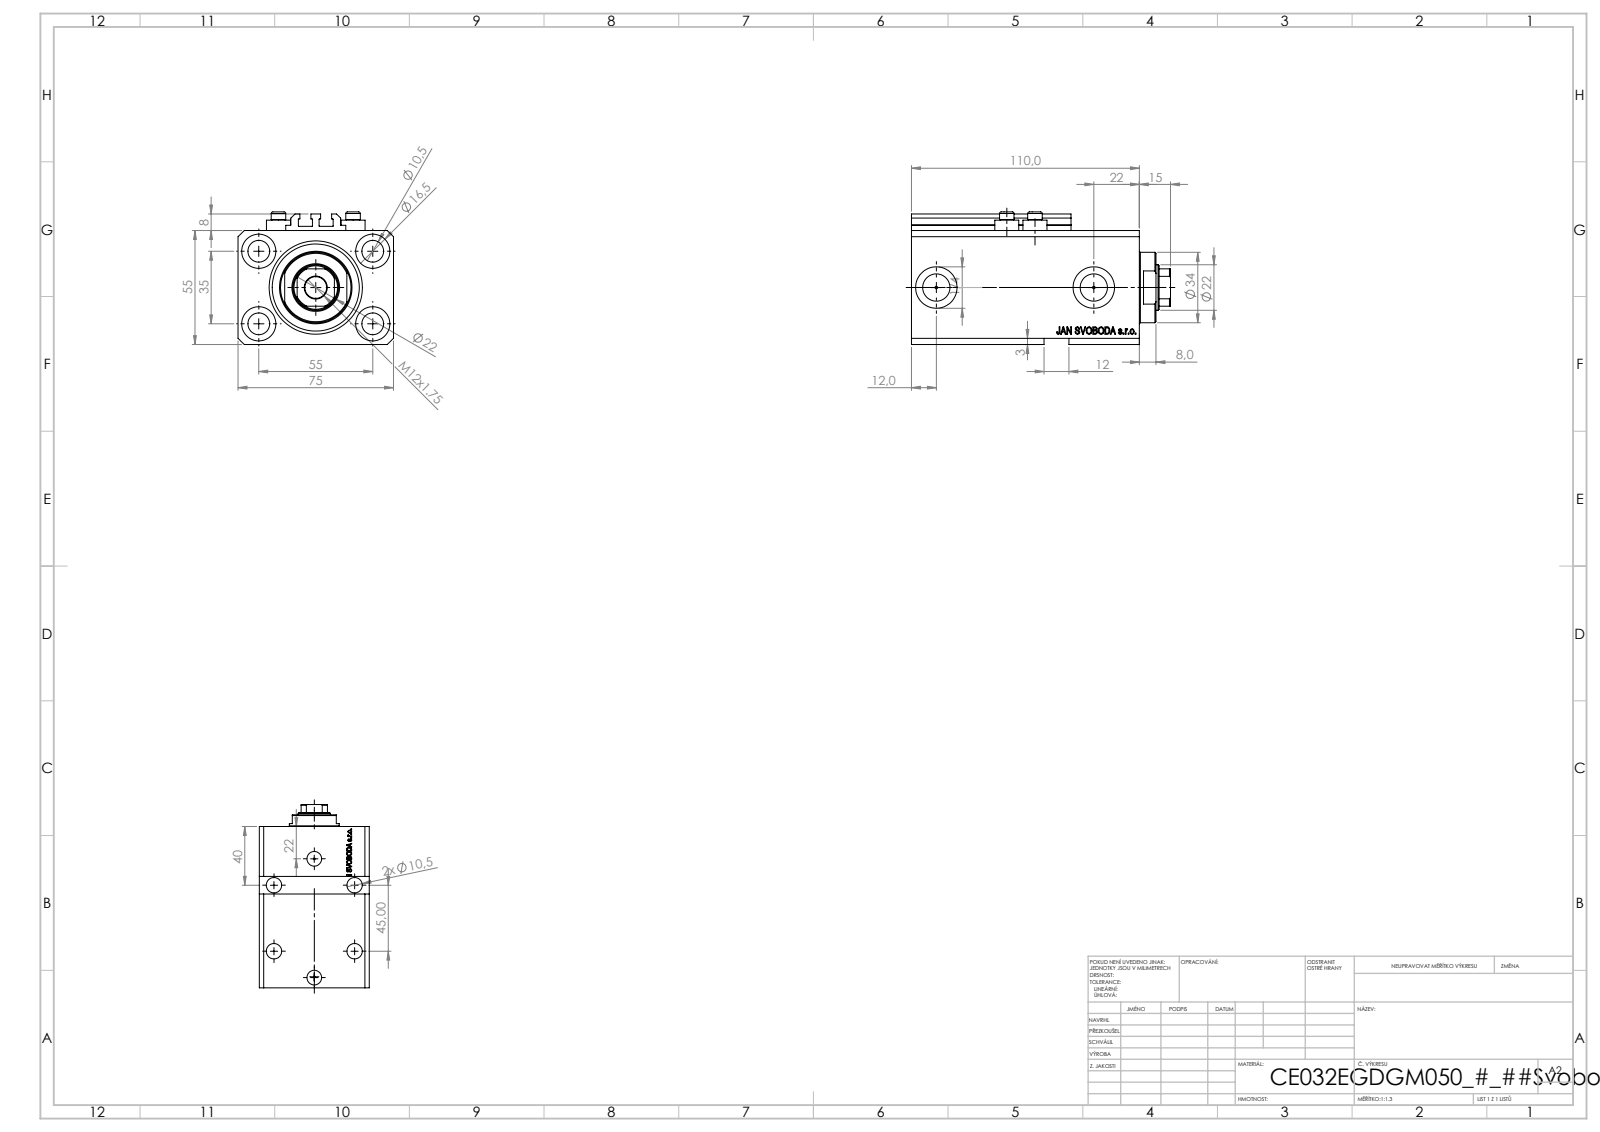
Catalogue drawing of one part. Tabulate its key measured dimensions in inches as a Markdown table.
| quantity | value |
| --- | --- |
| part name | V250CE_E_Body; V250CE_C_VCP; V250CE_VC_E; ALLEN BOLT V250CE |
| STEP written by | SolidWorks 2019 (CONFIG_CONTROL_DESIGN) |
| units | inches |
| bodies | 8 solids, 1100 faces (518 planar, 158 cylindrical, 424 other) |
| overall size | 4.921 × 2.953 × 2.52 |
| volume | 23.05 in³ |
| surface area | 150 in² |
| round holes (diameter × count) | 0.413 × 9, 0.049 × 4, 0.157 × 4, 0.65 × 4, 0.394 × 2, 0.518 × 2, 0.787 × 2, 0.866 × 1, 1.26 × 1, 1.772 × 1 |
| round bosses / shafts (diameter × count) | 0.457 × 4, 0.276 × 4, 1.339 × 1 |
| partial cylindrical surfaces (radius × count) | 0.008 × 10, 0.413 × 1 |
| main face-to-face distances | 2.165, 2.953, 0.591, 4.331, 3.74, 0.39, 0.118, 3.35, 3.941, 2.244 |
| hole center spacings | 1.283, 1.294, 2.165, 2.706, 0.535, 0.555, 0.907, 1.016 |
